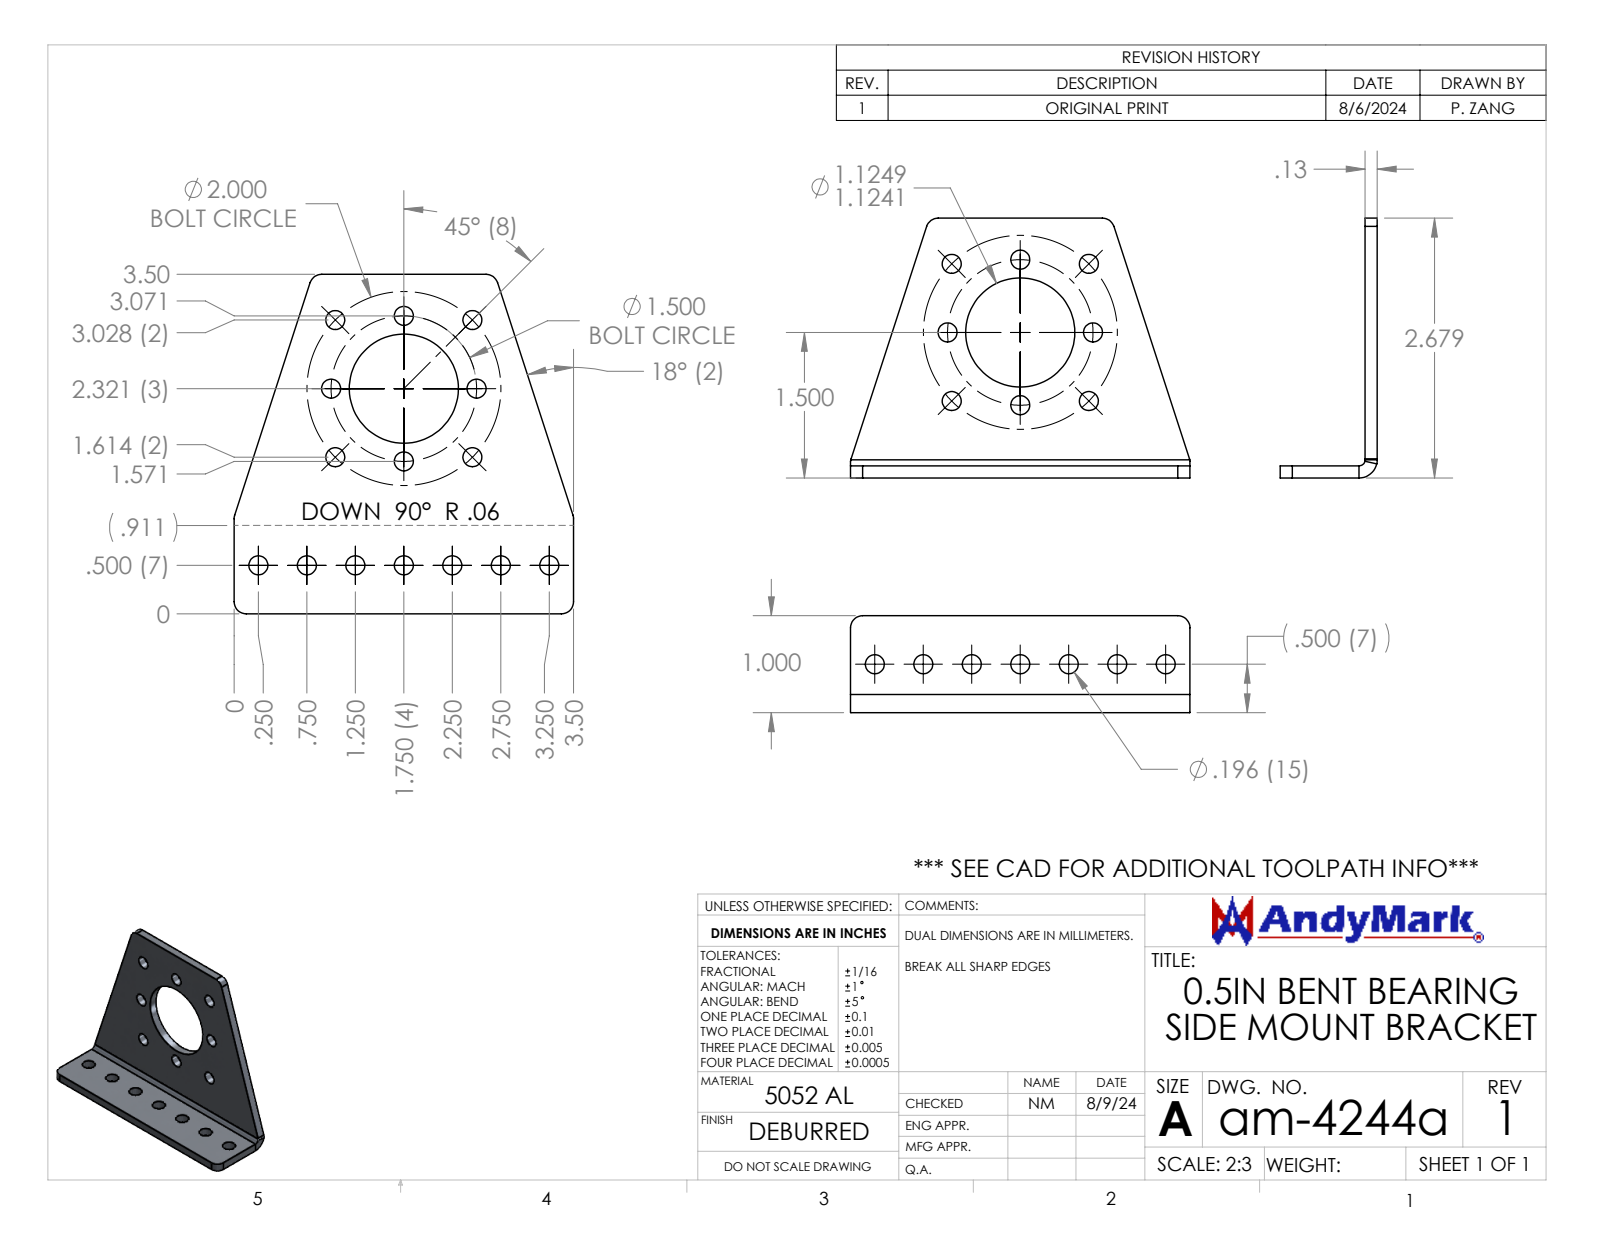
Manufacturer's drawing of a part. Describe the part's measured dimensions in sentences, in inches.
The part is named "am-4244a 0.5IN Bearing Bent Side Mount Gusset". Its 3-D file was written by "SolidWorks 2024 (CONFIG_CONTROL_DESIGN)". It is 1 solid with 54 faces: 12 planar, 40 cylindrical and 2 other. Overall it measures 3.5 by 2.679 by 1 inches. Its volume is 1.095 cubic inches and its surface area 20.68 square inches. Round holes: 15 of diameter 0.196, 1 of diameter 1.125. Partial cylindrical surfaces (rounded edges, fillets, slot ends): 6 of radius 0.125, 1 of radius 0.062, 1 of radius 0.187. The main face-to-face distances are 0.125, 1, 0.875, 2.679, 2.554, 3.5. The hole center spacings are 1, 0.708, 1.62, 0.5, 1.5, 2, 0.75, 1.061.
